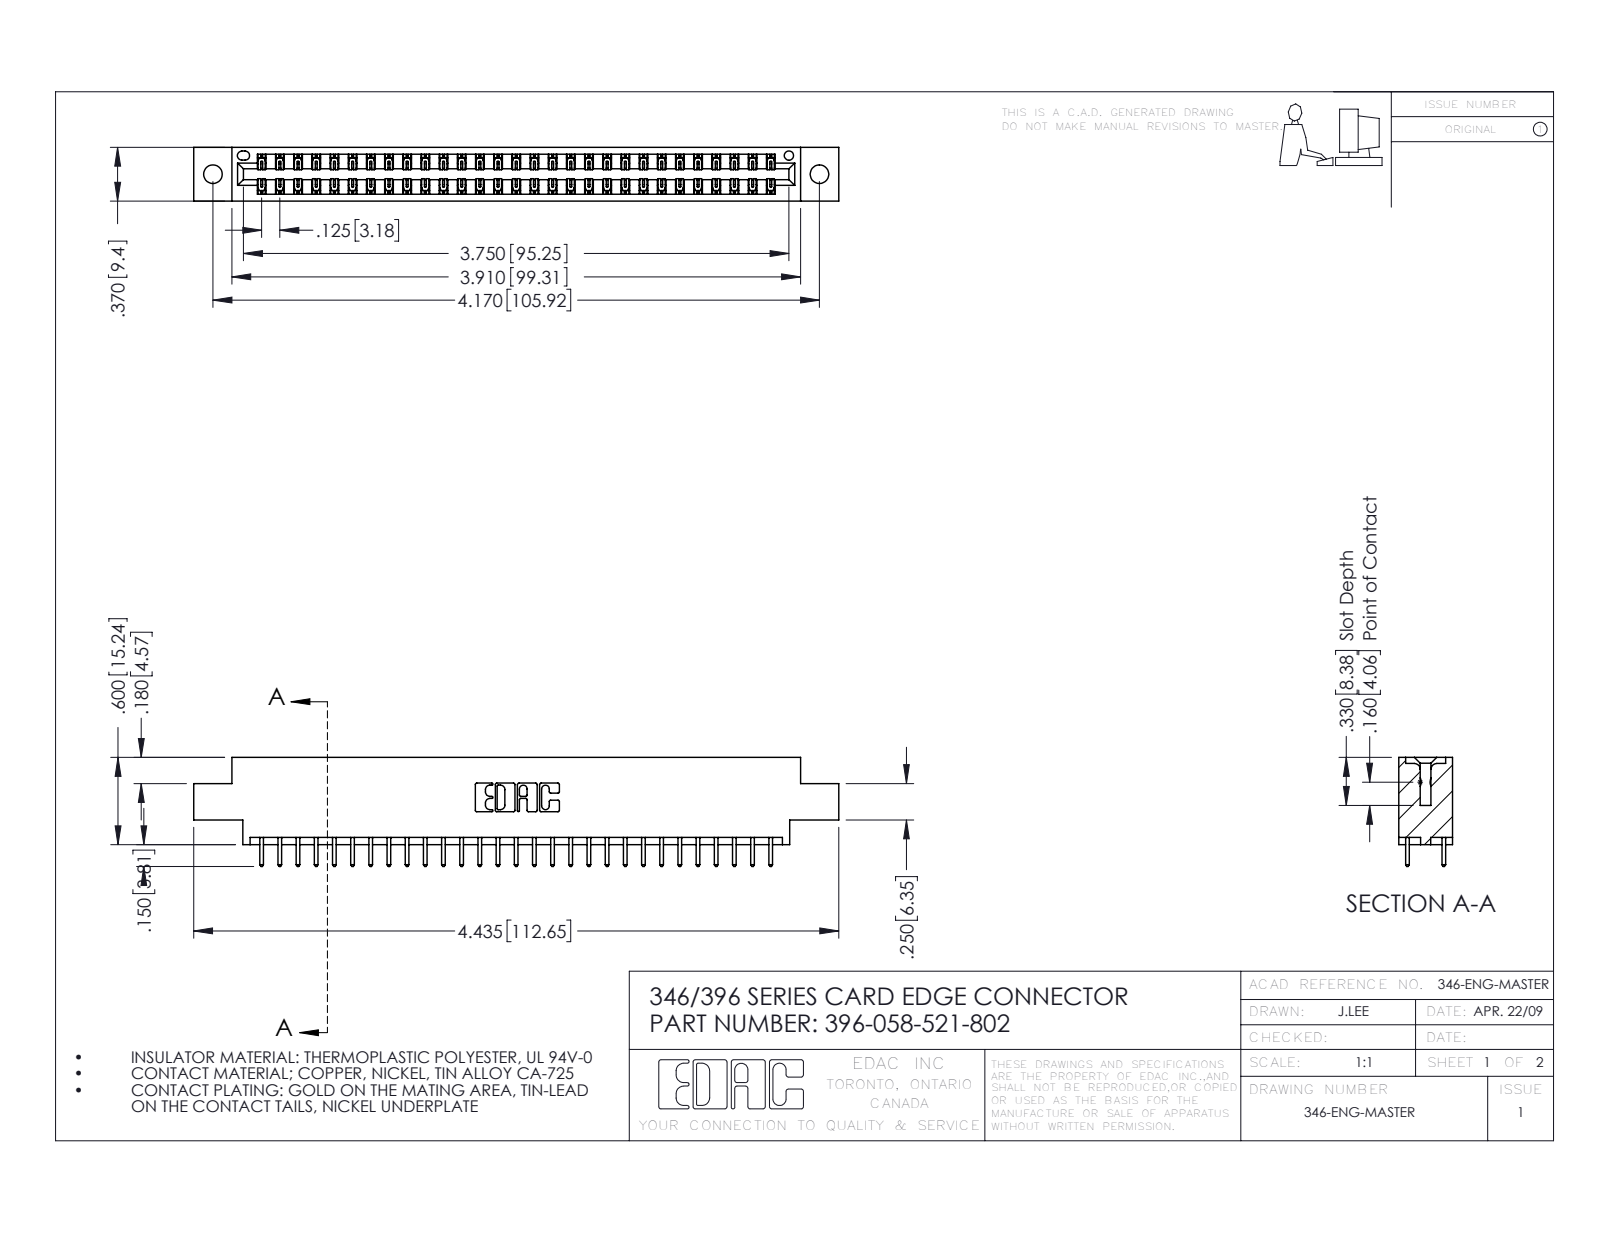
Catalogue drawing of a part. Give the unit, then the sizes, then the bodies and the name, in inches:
Units: inches
Overall size (bounding box): 4.435 × 0.75 × 0.37
Round holes (diameter × count): ⌀0.128 ×2, ⌀0.064 ×1
Partial cylindrical surfaces — rounded edges, fillets, slot ends (radius × count): R0.006 ×87, R0.01 ×58, R0.01 ×22, R0.007 ×6, R0.031 ×6, R0.026 ×3, R0.014 ×2, R0.022 ×2
Main face-to-face distances: 0.048, 0.322, 0.37, 0.25, 0.072, 0.298, 0.025, 0.275, 0.148, 0.222
Hole centre spacings: 0.246, 3.962, 4.17
Volume: 0.651 in³ · Surface area: 22.03 in²
Bodies: 59 solids, 3142 faces (2110 planar, 1032 cylindrical, 0 other)
Part name (STEP PRODUCT): 346 Part_0.170 Offset - 0.128 Dia; 345-292-001_345-293-121; 396-058-521-802
STEP written by: SolidWorks 2016 (CONFIG_CONTROL_DESIGN)
